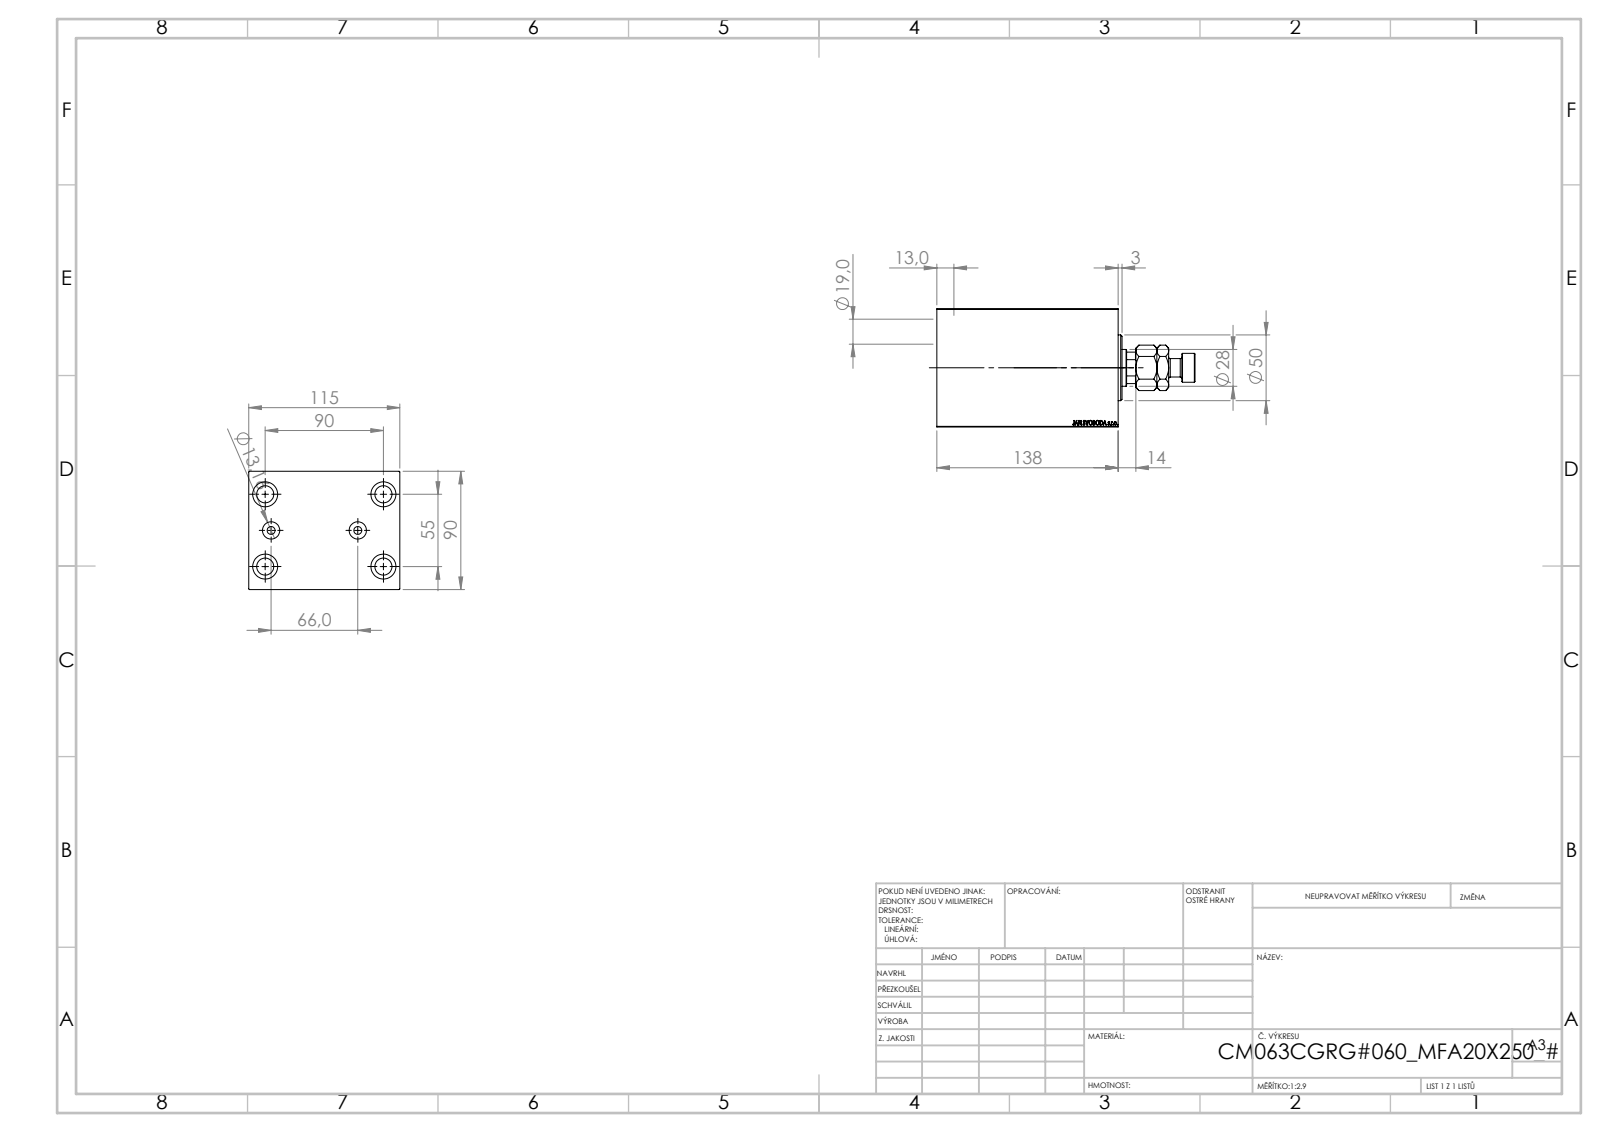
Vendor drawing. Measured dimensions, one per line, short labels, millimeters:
name: V450CM_VC_B; V450CM_C_Body; MFA; V450CM_C_VCP
written by: SolidWorks 2019 (CONFIG_CONTROL_DESIGN)
unit: mm
bodies: 4 solids, 913 faces (425 planar, 62 cylindrical, 426 other)
size: 196.5 × 115 × 90
volume: 1 210 000 mm³; area: 172 066 mm²
holes: 4× ⌀13, 4× ⌀19, 2× ⌀6, 2× ⌀13.16, 1× ⌀18.5, 1× ⌀28, 1× ⌀31.5, 1× ⌀63, 1× ⌀65, 1× ⌀72
bosses: 1× ⌀50, 1× ⌀22, 1× ⌀14
rounds: 1× R13.5
face distances: 90, 115, 138, 17.5, 120.5, 29.3, 91.2, 108.7, 89.3, 60
hole spacings: 30, 52.74, 82.71, 33, 55, 90, 105.48, 66
